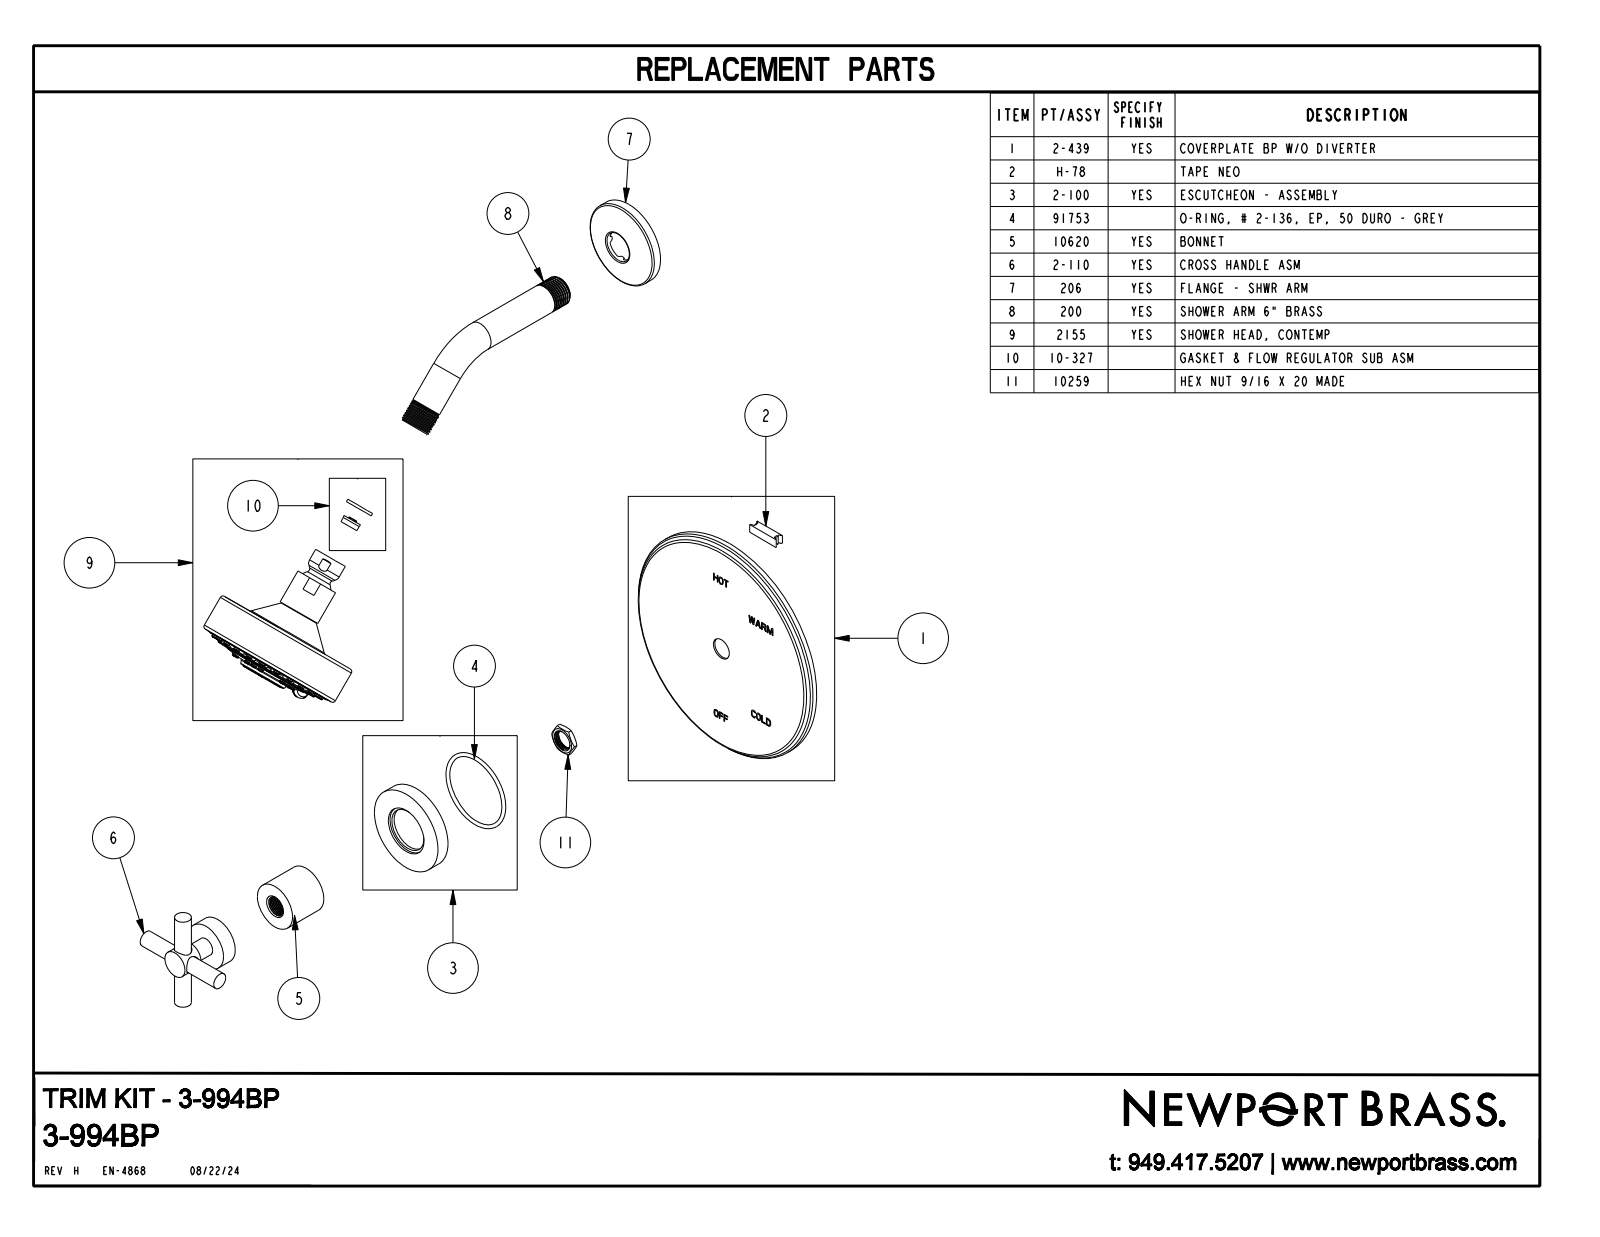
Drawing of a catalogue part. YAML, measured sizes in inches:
part_name: "3-994BP"
step_written_by: "CREO PARAMETRIC BY PTC INC, 2018400 (CONFIG_CONTROL_DESIGN)"
units: inches
bodies: {solids: 2, faces: 1421, planar: 474, cylindrical: 220, other: 727}
overall_size: [16.44, 8.175, 6.5]
volume: 35.44
surface_area: 165.6
round_holes:
  - {diameter: 0.059, count: 8}
  - {diameter: 0.47, count: 2}
  - {diameter: 0.925, count: 1}
round_bosses_or_shafts:
  - {diameter: 0.142, count: 39}
  - {diameter: 0.165, count: 23}
  - {diameter: 0.813, count: 2}
  - {diameter: 0.445, count: 2}
  - {diameter: 6.5, count: 1}
  - {diameter: 4, count: 1}
  - {diameter: 3.724, count: 1}
  - {diameter: 2.38, count: 1}
partial_cylinders:
  - {radius: 0.079, count: 8}
  - {radius: 0.02, count: 2}
  - {radius: 0.138, count: 1}
  - {radius: 0.472, count: 1}
  - {radius: 0.512, count: 1}
  - {radius: 0.63, count: 1}
face_to_face_distances: [0.313, 0.688, 0.375, 0.02, 1.503, 1.796, 1.816, 1.483, 1.108, 1.128]
hole_center_spacings: [0.443, 0.579, 0.818, 0.819, 1.069, 0.443, 0.578, 1.069]
